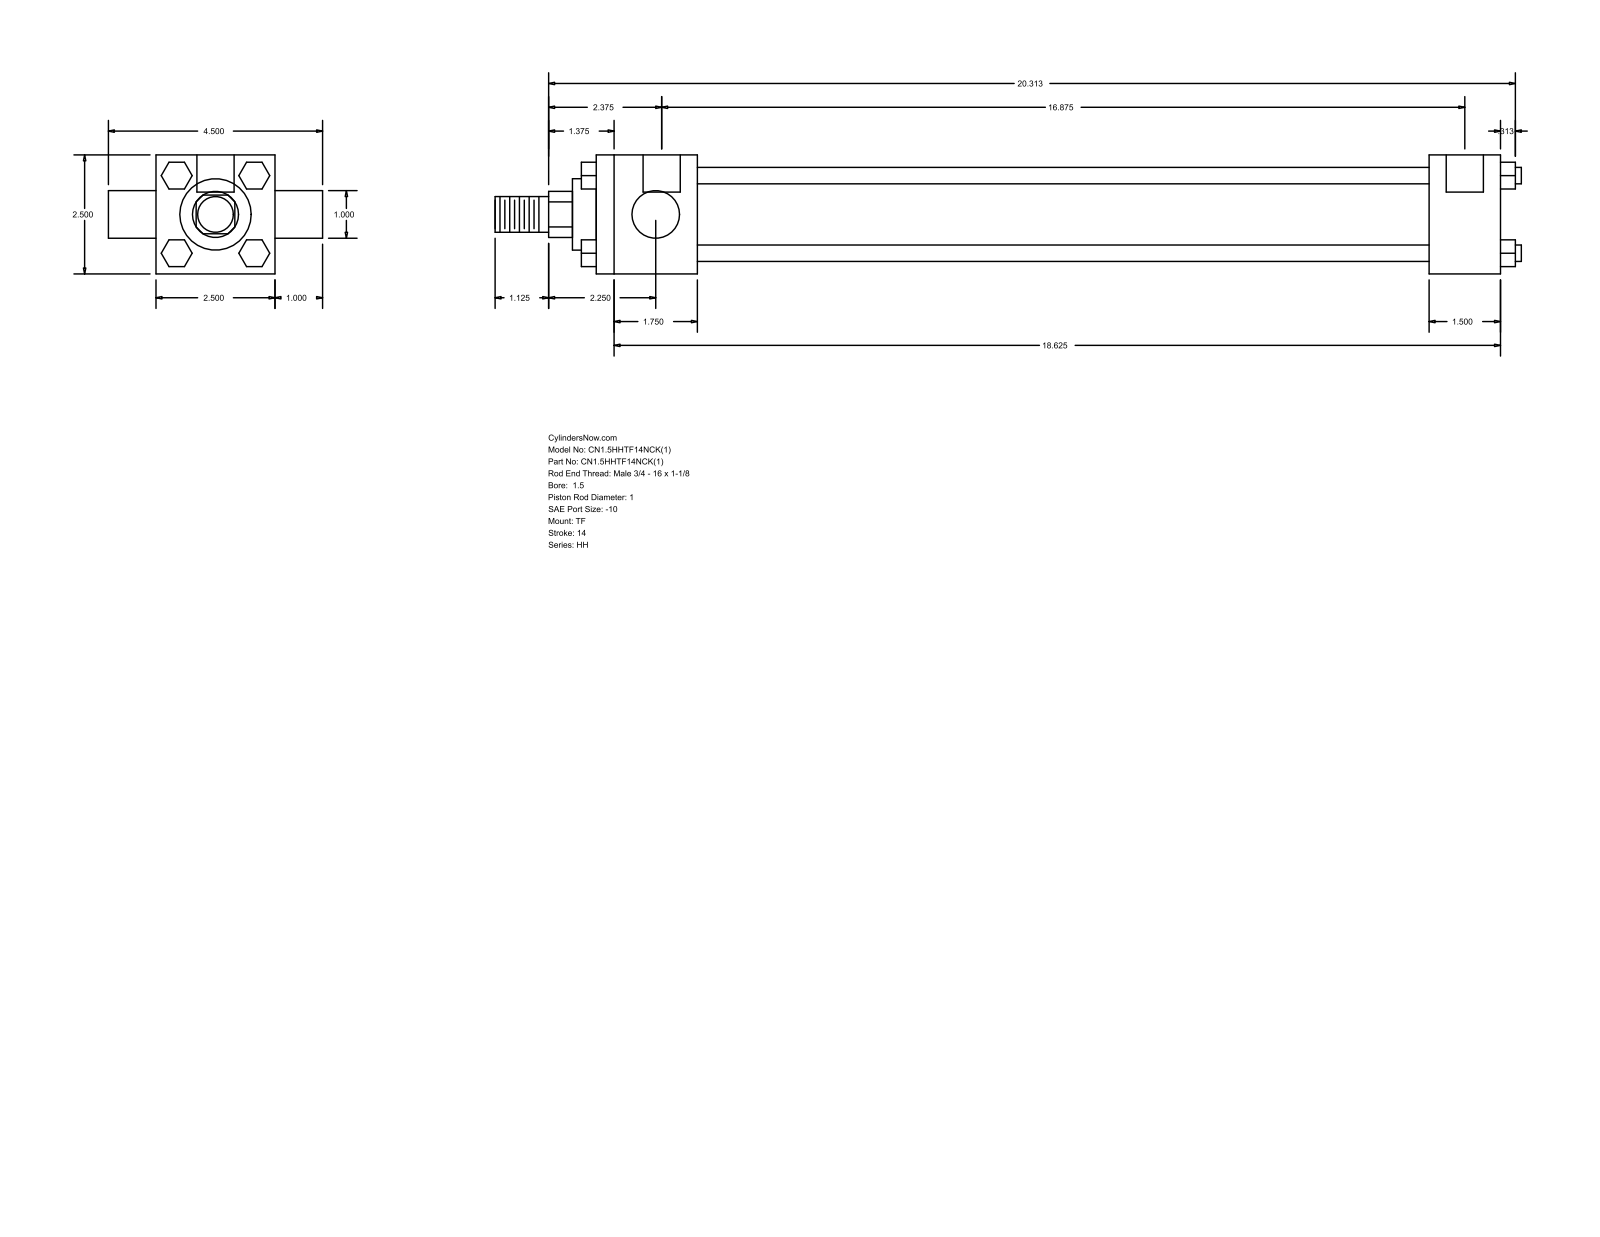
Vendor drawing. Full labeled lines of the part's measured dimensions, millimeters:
Part name (STEP PRODUCT): HH_TF__0150_1
STEP written by: GSSL Pune (CONFIG_CONTROL_DESIGN)
Units: millimetres
Bodies: 0 solids, 120 faces (92 planar, 28 cylindrical, 0 other)
Overall size (bounding box): 547.69 × 114.3 × 63.5
Round holes (diameter × count): ⌀5.56 ×3, ⌀19.84 ×2
Round bosses / shafts (diameter × count): ⌀8.76 ×4, ⌀25.4 ×2, ⌀44.45 ×1, ⌀38.1 ×1, ⌀19.05 ×1
Partial cylindrical surfaces — rounded edges, fillets, slot ends (radius × count): R12.29 ×1
Main face-to-face distances: 63.5, 38.1, 428.62, 390.52, 53.98, 444.5, 482.6, 25.4, 20.7, 14.29
Hole centre spacings: 1.59, 430.21, 428.62, 431.8
